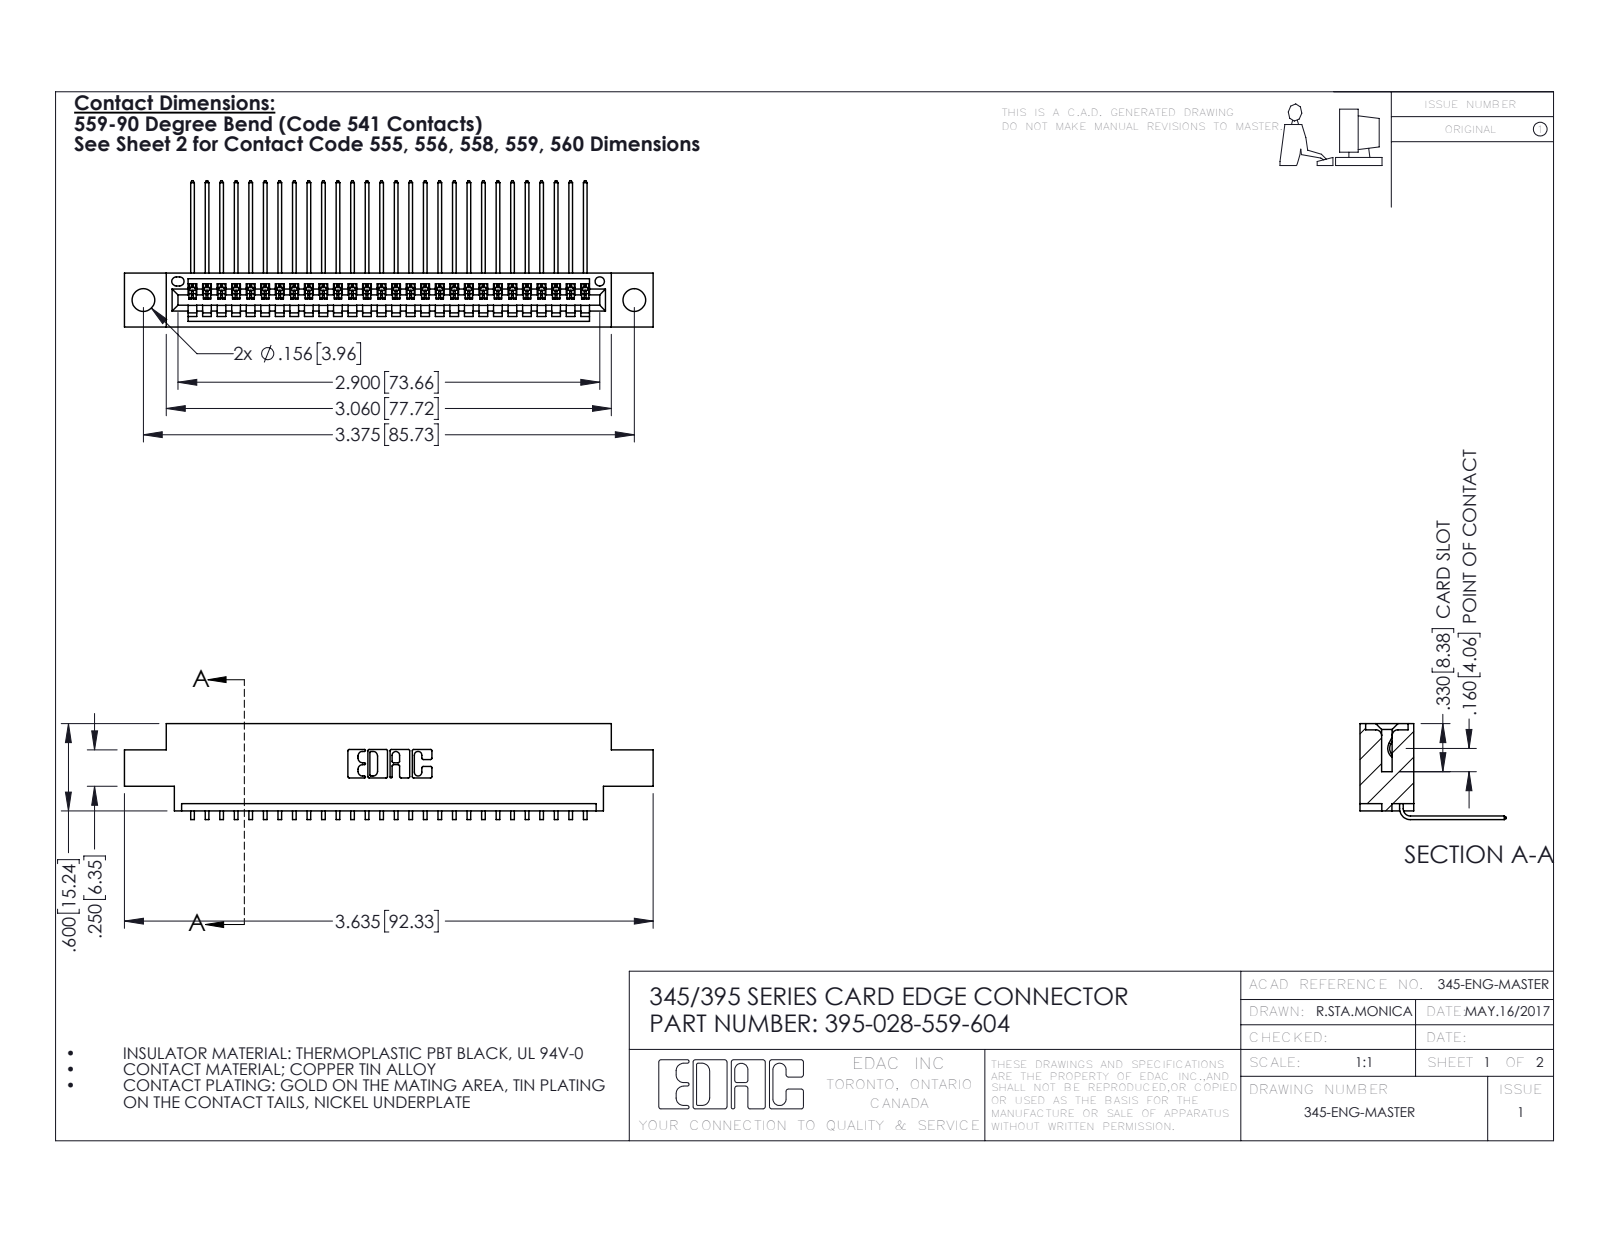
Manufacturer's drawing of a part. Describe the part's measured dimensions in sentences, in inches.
The part is named "345-292-001_558 559 Tail - 1; 345 Part_0.170 Offset - 0.156 Dia-TH; 395-028-559-604". Its 3-D file was written by "SolidWorks 2016 (CONFIG_CONTROL_DESIGN)". It is 29 solids with 1810 faces: 1260 planar, 550 cylindrical and 0 other. Overall it measures 3.635 by 1.005 by 0.659 inches. Its volume is 0.522 cubic inches and its surface area 18.06 square inches. Round holes: 2 of diameter 0.156, 1 of diameter 0.064. Partial cylindrical surfaces (rounded edges, fillets, slot ends): 56 of radius 0.006, 22 of radius 0.01, 6 of radius 0.007, 6 of radius 0.031, 3 of radius 0.026, 2 of radius 0.031, 2 of radius 0.04, 1 of radius 0.014. The main face-to-face distances are 0.072, 0.298, 0.37, 0.2, 0.098, 0.272, 0.025, 0.225, 0.175, 0.149. The hole center spacings are 0.27, 3.14, 3.375.
